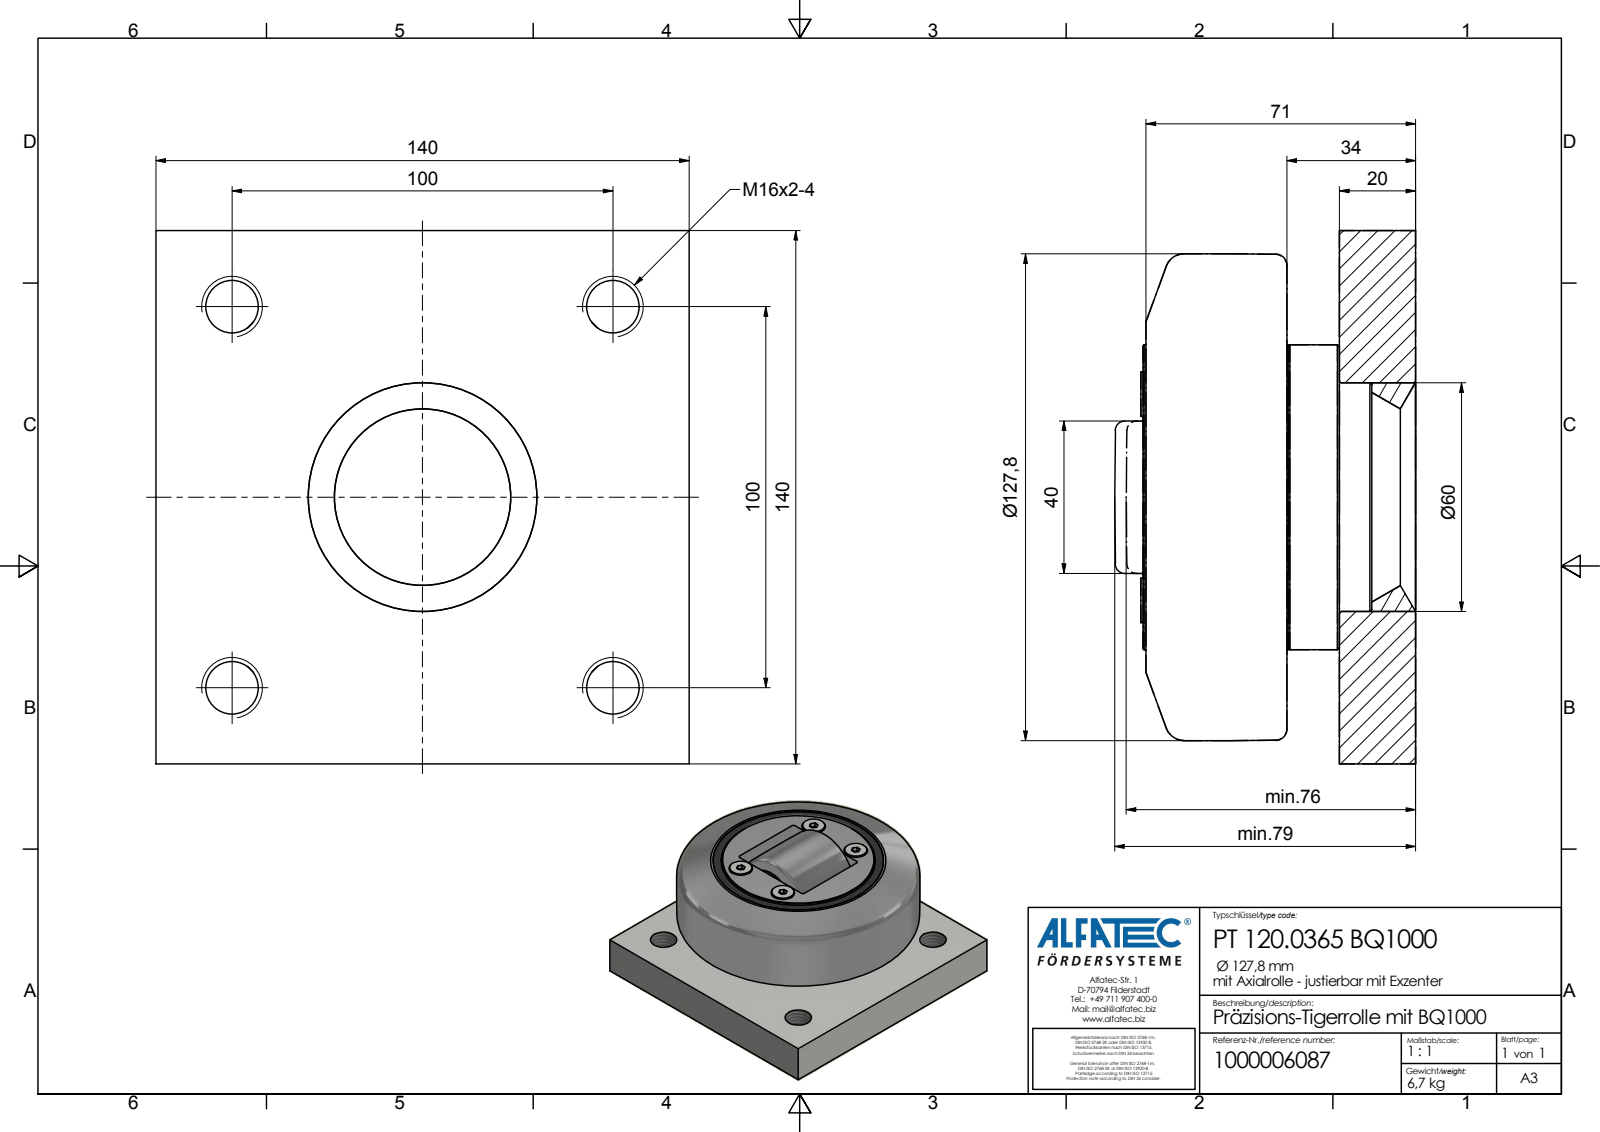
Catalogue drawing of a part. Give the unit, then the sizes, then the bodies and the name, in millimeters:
Units: millimetres
Overall size (bounding box): 140 × 140 × 79
Round holes (diameter × count): ⌀6.6 ×4, ⌀13.84 ×4, ⌀3 ×1, ⌀28.5 ×1, ⌀33.5 ×1, ⌀81 ×1, ⌀87 ×1, ⌀89.5 ×1, ⌀95 ×1
Round bosses / shafts (diameter × count): ⌀11.7 ×4, ⌀6 ×4, ⌀86 ×1, ⌀84.5 ×1, ⌀80 ×1, ⌀79 ×1, ⌀71 ×1, ⌀69.9 ×1
Partial cylindrical surfaces — rounded edges, fillets, slot ends (radius × count): R1 ×8, R21.3 ×2, R25.5 ×1
Main face-to-face distances: 20, 140, 33.8, 13.8, 37.8, 71.6, 51.6, 49, 91, 1
Hole centre spacings: 31.24, 41.33, 69.51, 70.71, 84.38, 100, 101.21, 54.12
Volume: 816 399 mm³ · Surface area: 132 035 mm²
Bodies: 2 solids, 268 faces (183 planar, 54 cylindrical, 31 other)
Part name (STEP PRODUCT): PT 120.0365 BQ1000_Kontur
STEP written by: Autodesk Inventor 2020 (AUTOMOTIVE_DESIGN)
